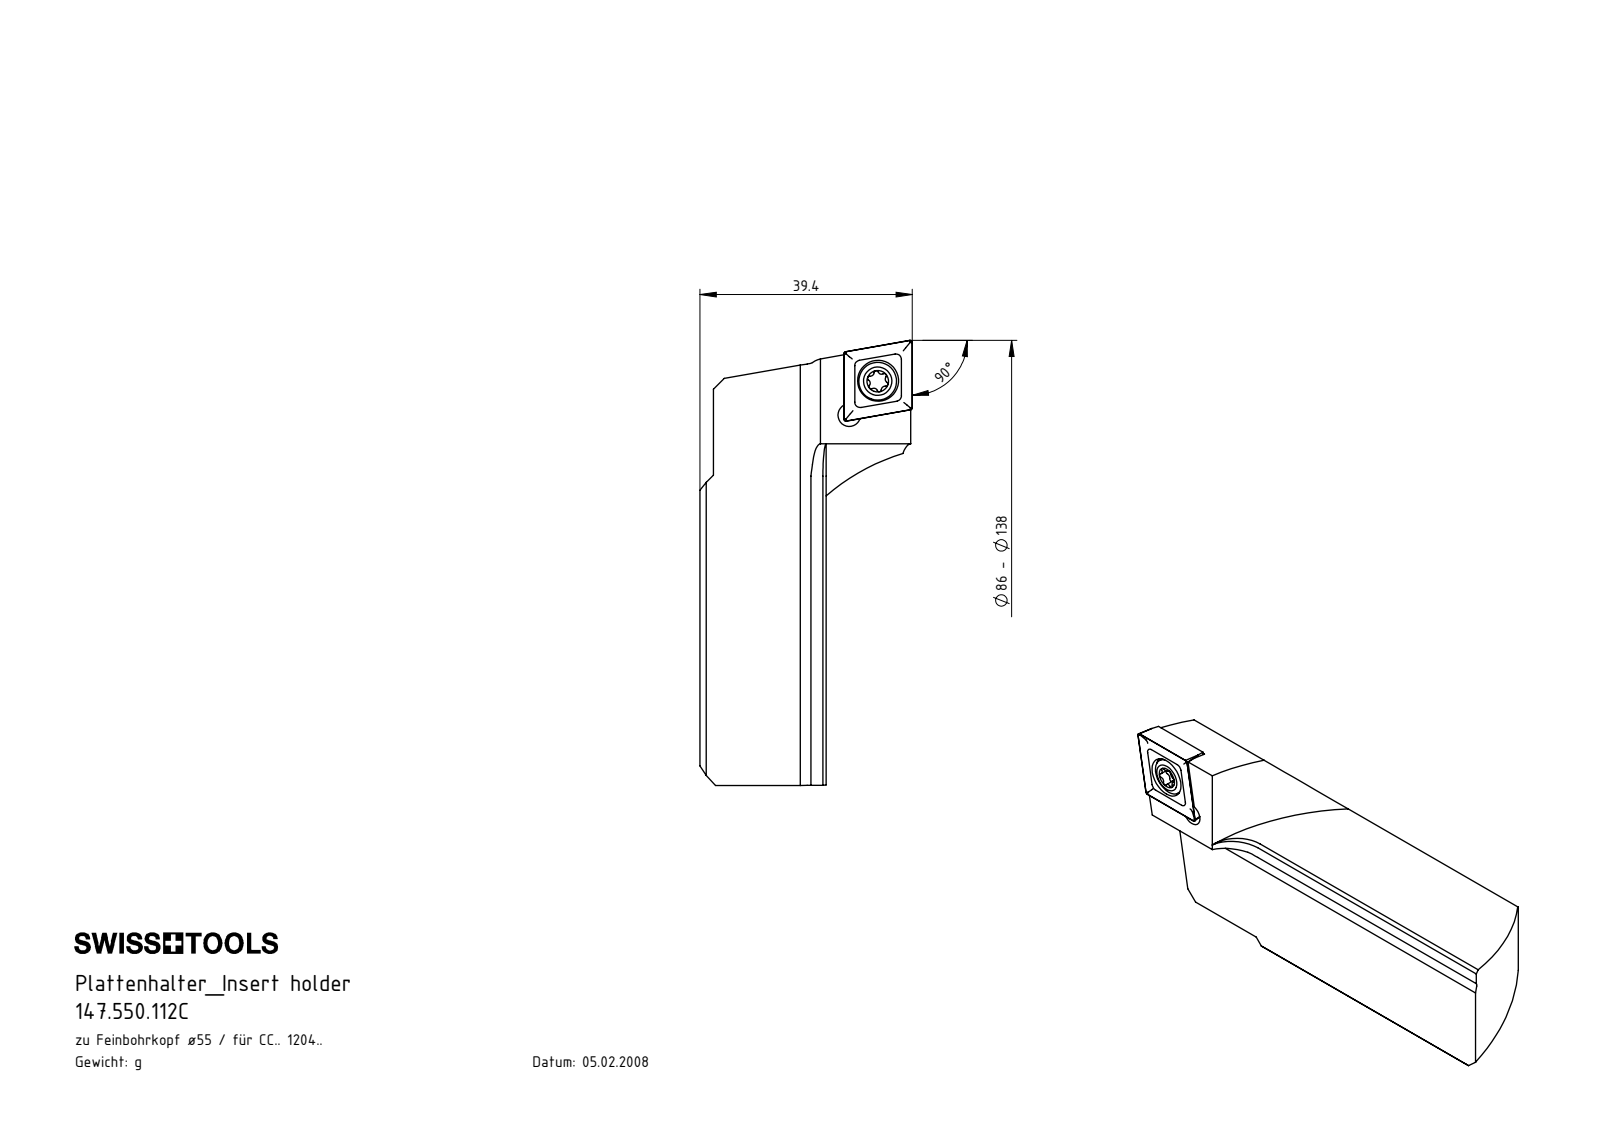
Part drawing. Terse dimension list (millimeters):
name: CCMT120404; F00-WCC.086.001_C; WCC-ER2.001.010_A; 147.550.112C
written by: SolidWorks 2017 (CONFIG_CONTROL_DESIGN)
unit: mm
bodies: 3 solids, 379 faces (226 planar, 40 cylindrical, 113 other)
size: 82.58 × 39.4 × 27.35
volume: 33 749 mm³; area: 9 364 mm²
holes: 2× ⌀4.2, 1× ⌀5.5, 1× ⌀7.6
bosses: 1× ⌀7, 1× ⌀5
rounds: 8× R0.2, 6× R0.39, 3× R0.69, 3× R0.69, 3× R40, 1× R0.8, 1× R6
face distances: 2.38, 21.3, 4.76, 7.14, 9.52, 4.77, 7.15, 9.53, 11.91, 14.29
hole spacings: 8.21, 8.33
